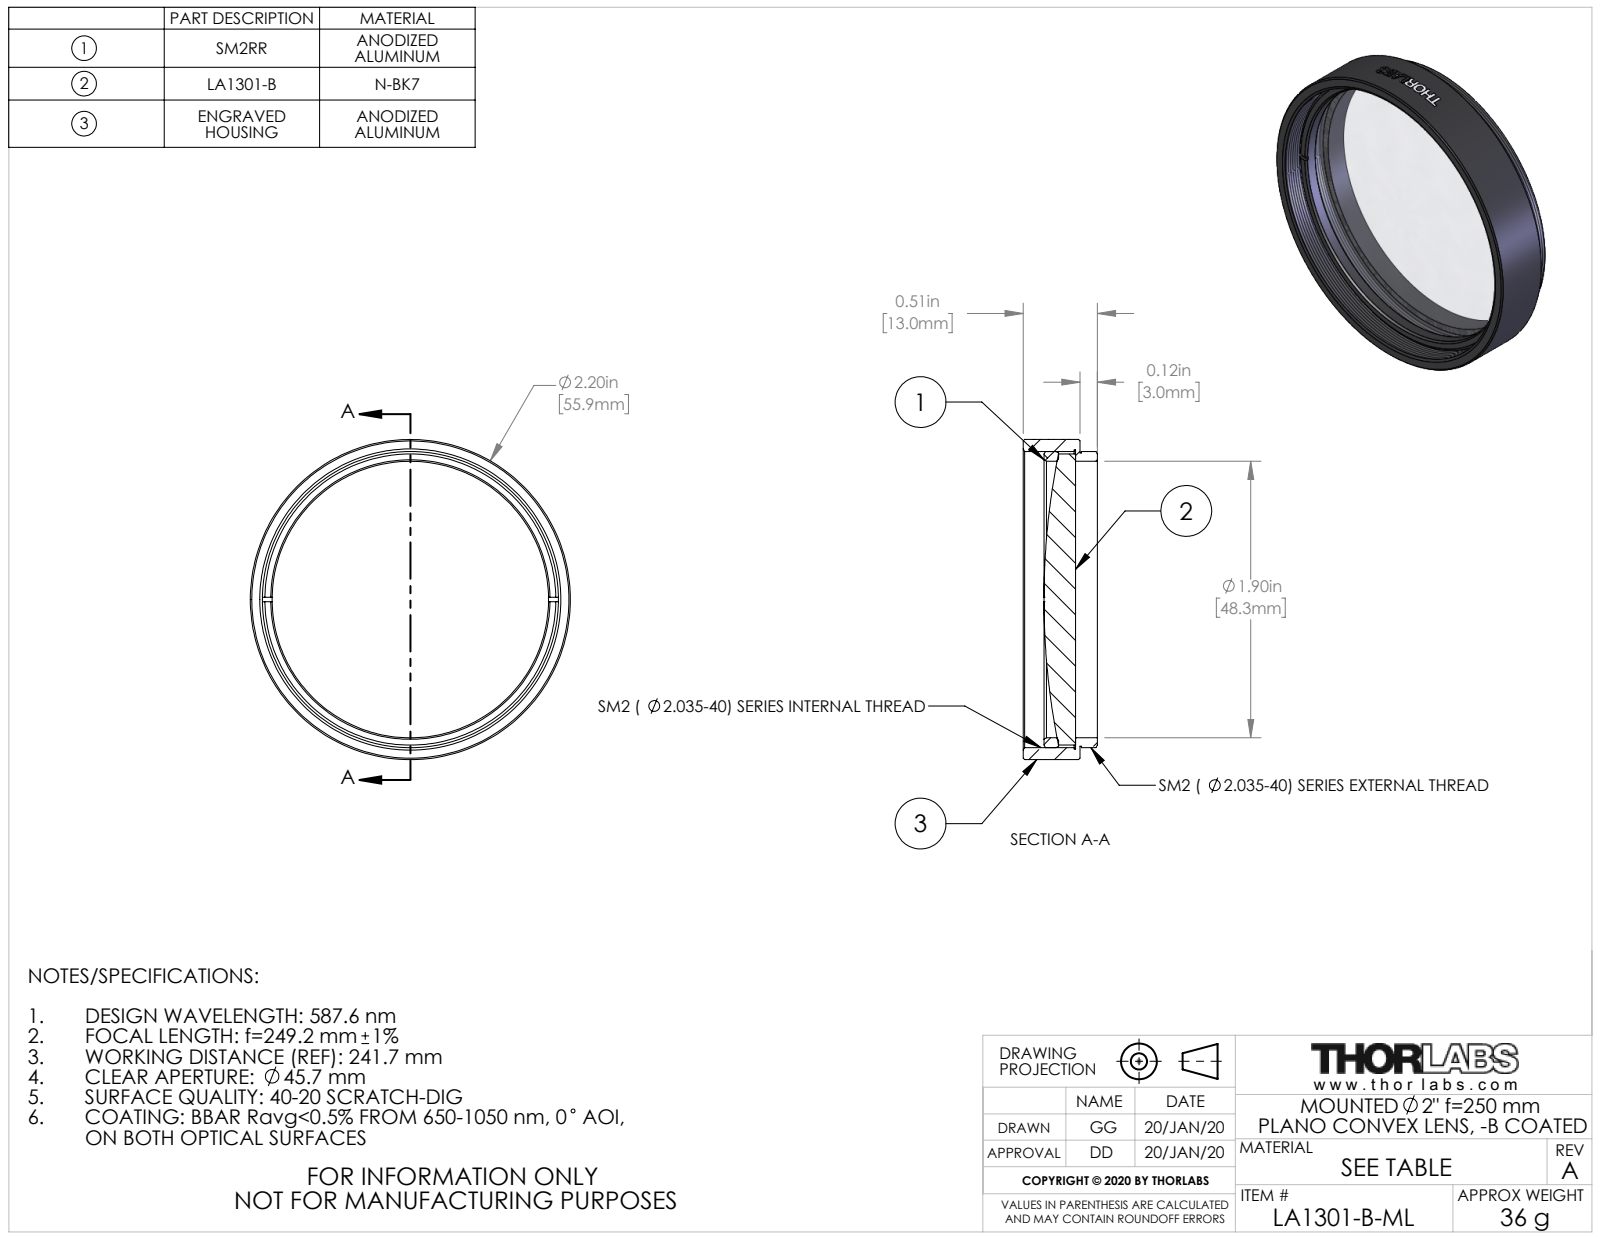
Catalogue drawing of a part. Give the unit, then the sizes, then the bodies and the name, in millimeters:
Units: millimetres
Overall size (bounding box): 55.88 × 55.88 × 12.95
Round holes (diameter × count): ⌀48.26 ×1, ⌀52.2 ×1
Round bosses / shafts (diameter × count): ⌀55.88 ×1, ⌀51.69 ×1, ⌀51.18 ×1, ⌀50.8 ×1
Main face-to-face distances: 0.76, 9.91, 9.15, 3.05, 3.81, 12.96, 6.8, 3.75, 2.99, 6.16
Volume: 13 761 mm³ · Surface area: 11 368 mm²
Bodies: 3 solids, 149 faces (16 planar, 113 cylindrical, 20 other)
Part name (STEP PRODUCT): TTN203753-E0W
STEP written by: SolidWorks 2018 (CONFIG_CONTROL_DESIGN)
